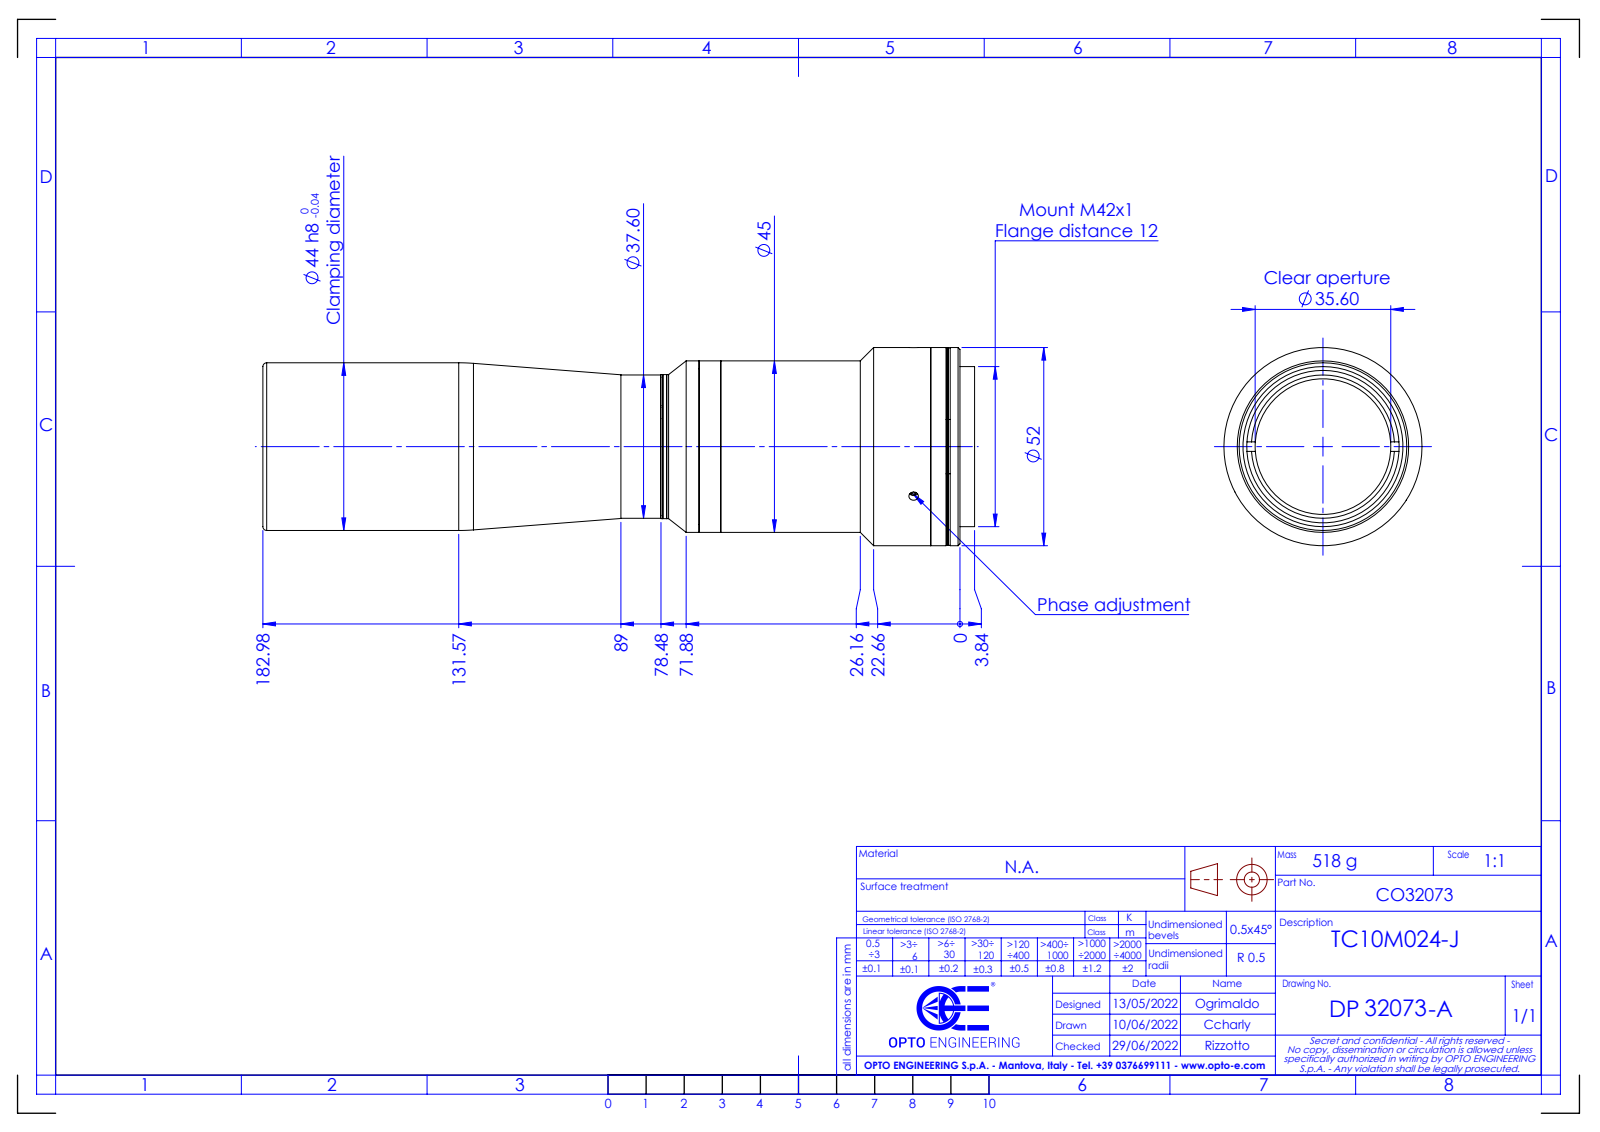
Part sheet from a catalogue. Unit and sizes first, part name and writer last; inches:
Units: inches
Overall size (bounding box): 7.355 × 2.047 × 2.047
Round holes (diameter × count): ⌀0.098 ×3, ⌀1.402 ×1, ⌀1.496 ×1, ⌀1.575 ×1, ⌀1.614 ×1
Round bosses / shafts (diameter × count): ⌀2.047 ×1, ⌀2.039 ×1, ⌀1.772 ×1, ⌀1.732 ×1, ⌀1.654 ×1, ⌀1.488 ×1, ⌀1.48 ×1
Main face-to-face distances: 0.201, 0.157, 0.043, 0.302, 0.144, 0.101, 0.181, 0.024, 0.02, 0.12
Bodies: 0 solids, 100 faces (30 planar, 46 cylindrical, 24 other)
Part name (STEP PRODUCT): DP32073-A_TC10M024-J
STEP written by: SolidWorks 2021 (CONFIG_CONTROL_DESIGN)
